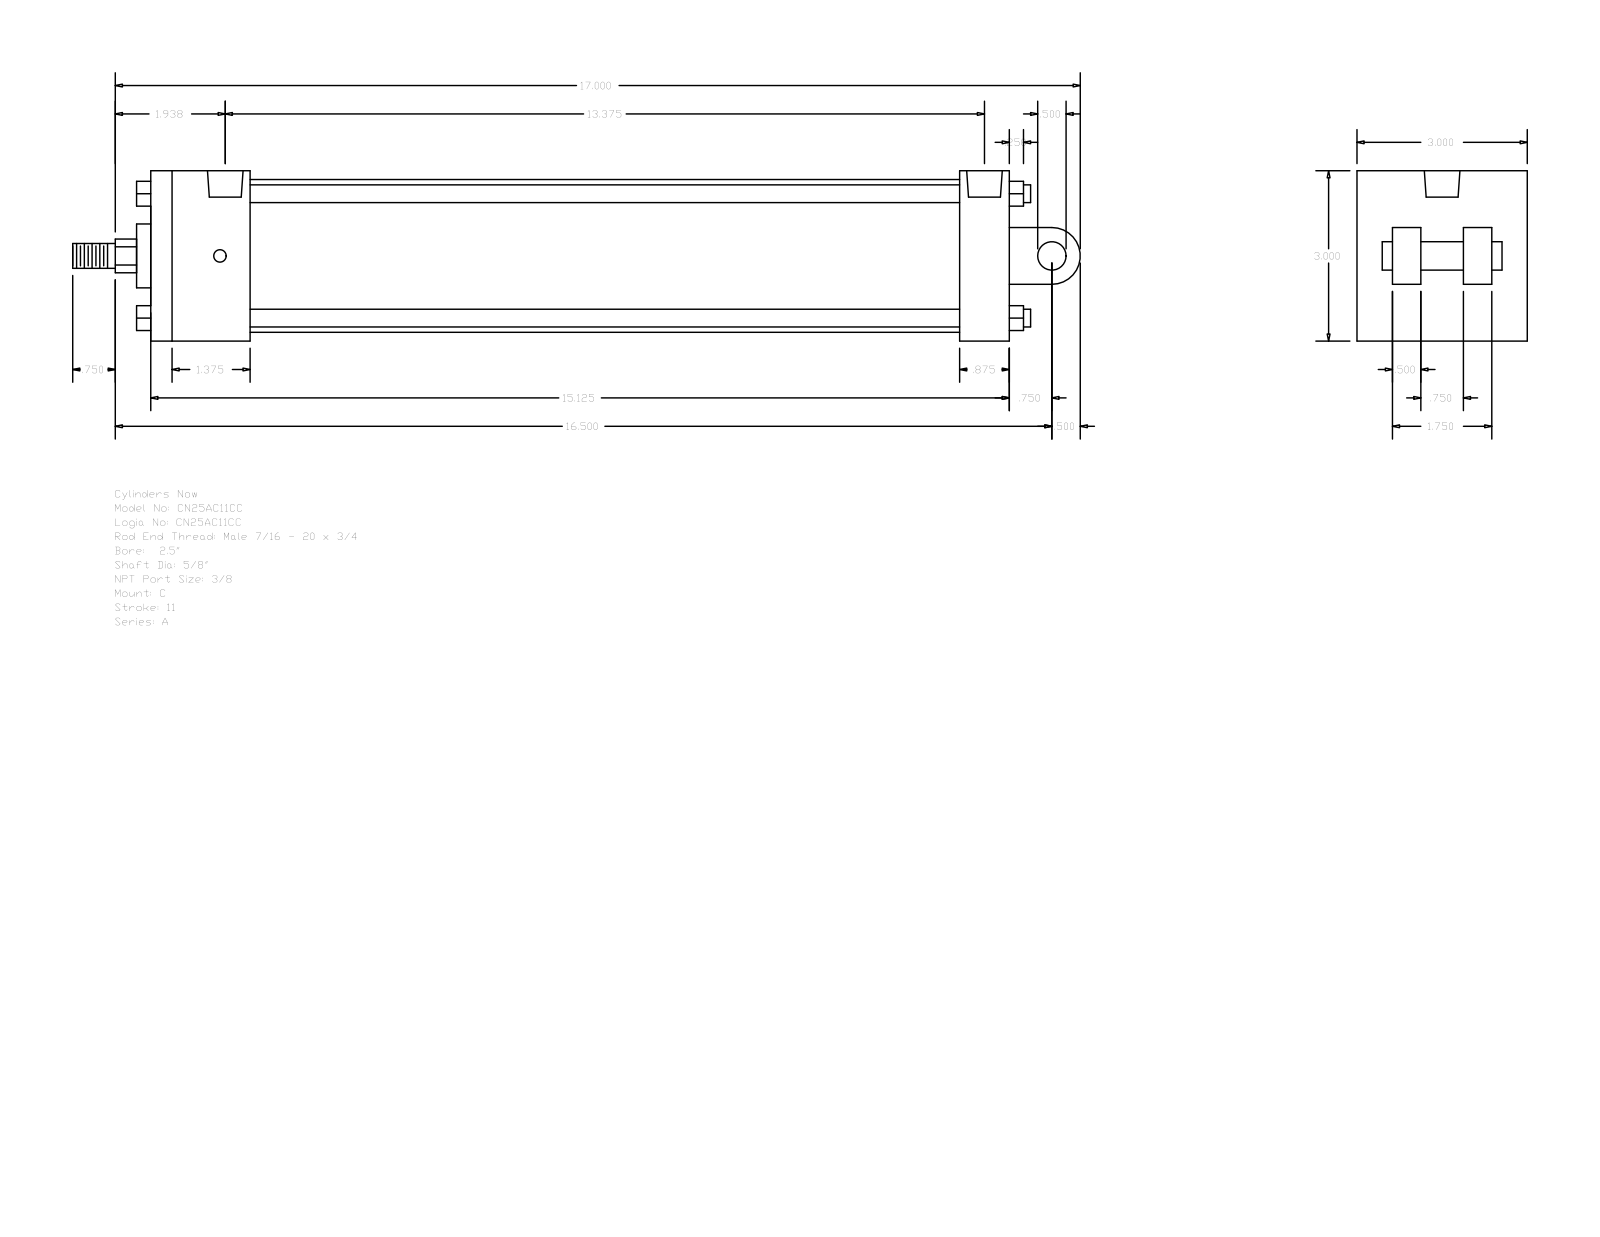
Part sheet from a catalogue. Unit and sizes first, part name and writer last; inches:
Units: inches
Overall size (bounding box): 17.75 × 3 × 3
Round holes (diameter × count): ⌀0.219 ×4, ⌀0.627 ×2
Round bosses / shafts (diameter × count): ⌀0.313 ×4, ⌀2.69 ×1, ⌀1.125 ×1, ⌀0.625 ×1, ⌀0.5 ×1, ⌀0.437 ×1
Partial cylindrical surfaces — rounded edges, fillets, slot ends (radius × count): R0.297 ×1, R0.5 ×1
Main face-to-face distances: 3, 15.125, 1.75, 14.25, 12.5, 13.375, 0.875, 2, 0.5, 1
Hole centre spacings: 0.094, 13.469, 13.563, 13.375
Bodies: 0 solids, 135 faces (102 planar, 33 cylindrical, 0 other)
Part name (STEP PRODUCT): A_C__0250_0.625
STEP written by: GSSL Pune (CONFIG_CONTROL_DESIGN)
